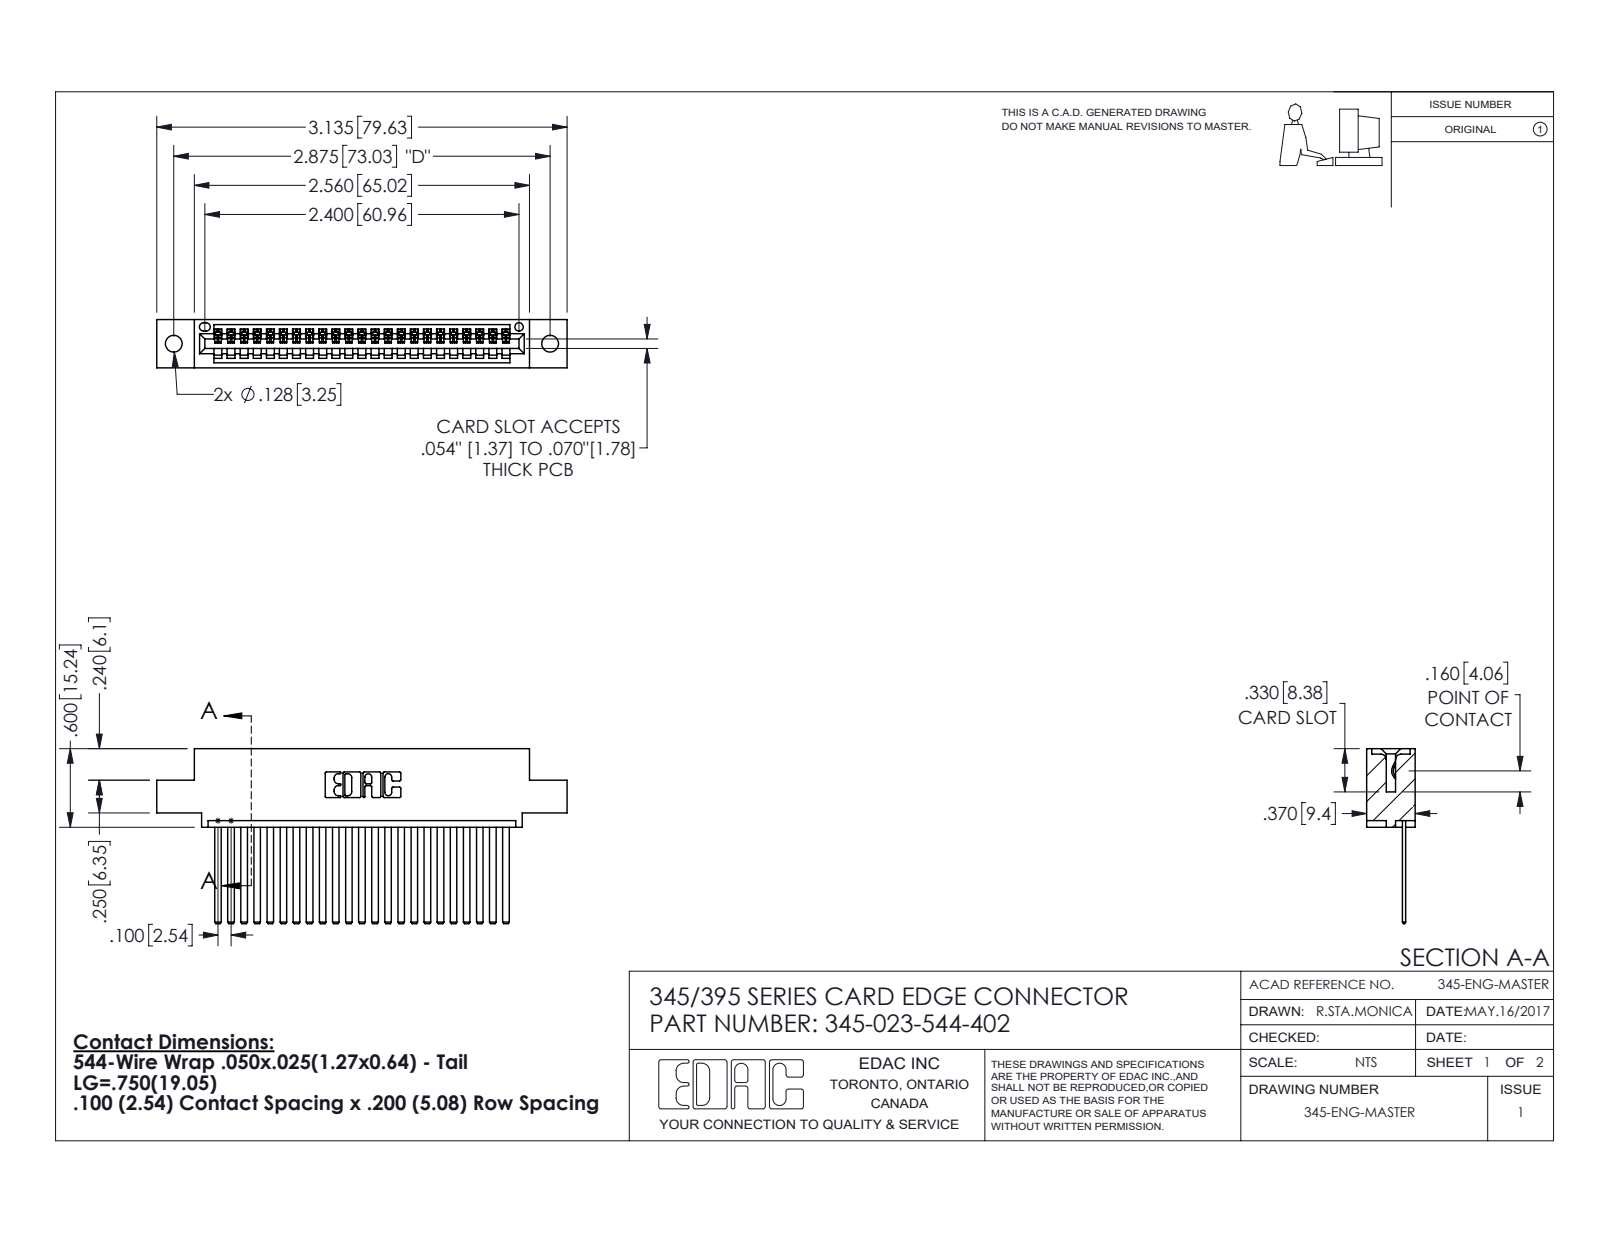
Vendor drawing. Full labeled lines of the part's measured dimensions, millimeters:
Part name (STEP PRODUCT): 345 Part_0.110 Offset - 0.128 Dia; 345-292-001_345-293-144; 345-023-544-402
STEP written by: SolidWorks 2016 (CONFIG_CONTROL_DESIGN)
Units: millimetres
Bodies: 24 solids, 1326 faces (912 planar, 414 cylindrical, 0 other)
Overall size (bounding box): 79.6 × 34 × 9.4
Volume: 7 570 mm³ · Surface area: 10 410 mm²
Round holes (diameter × count): ⌀3.3 ×2, ⌀1.6 ×1
Partial cylindrical surfaces — rounded edges, fillets, slot ends (radius × count): R0.2 ×46, R0.3 ×22, R0.2 ×6, R0.8 ×6, R0.7 ×3, R0.8 ×2, R1 ×2, R0.4 ×1
Main face-to-face distances: 1.8, 7.6, 2.5, 0.6, 6.9, 9.4, 5.1, 5.7, 3.8, 1.8
Hole centre spacings: 6.9, 67.1, 73
